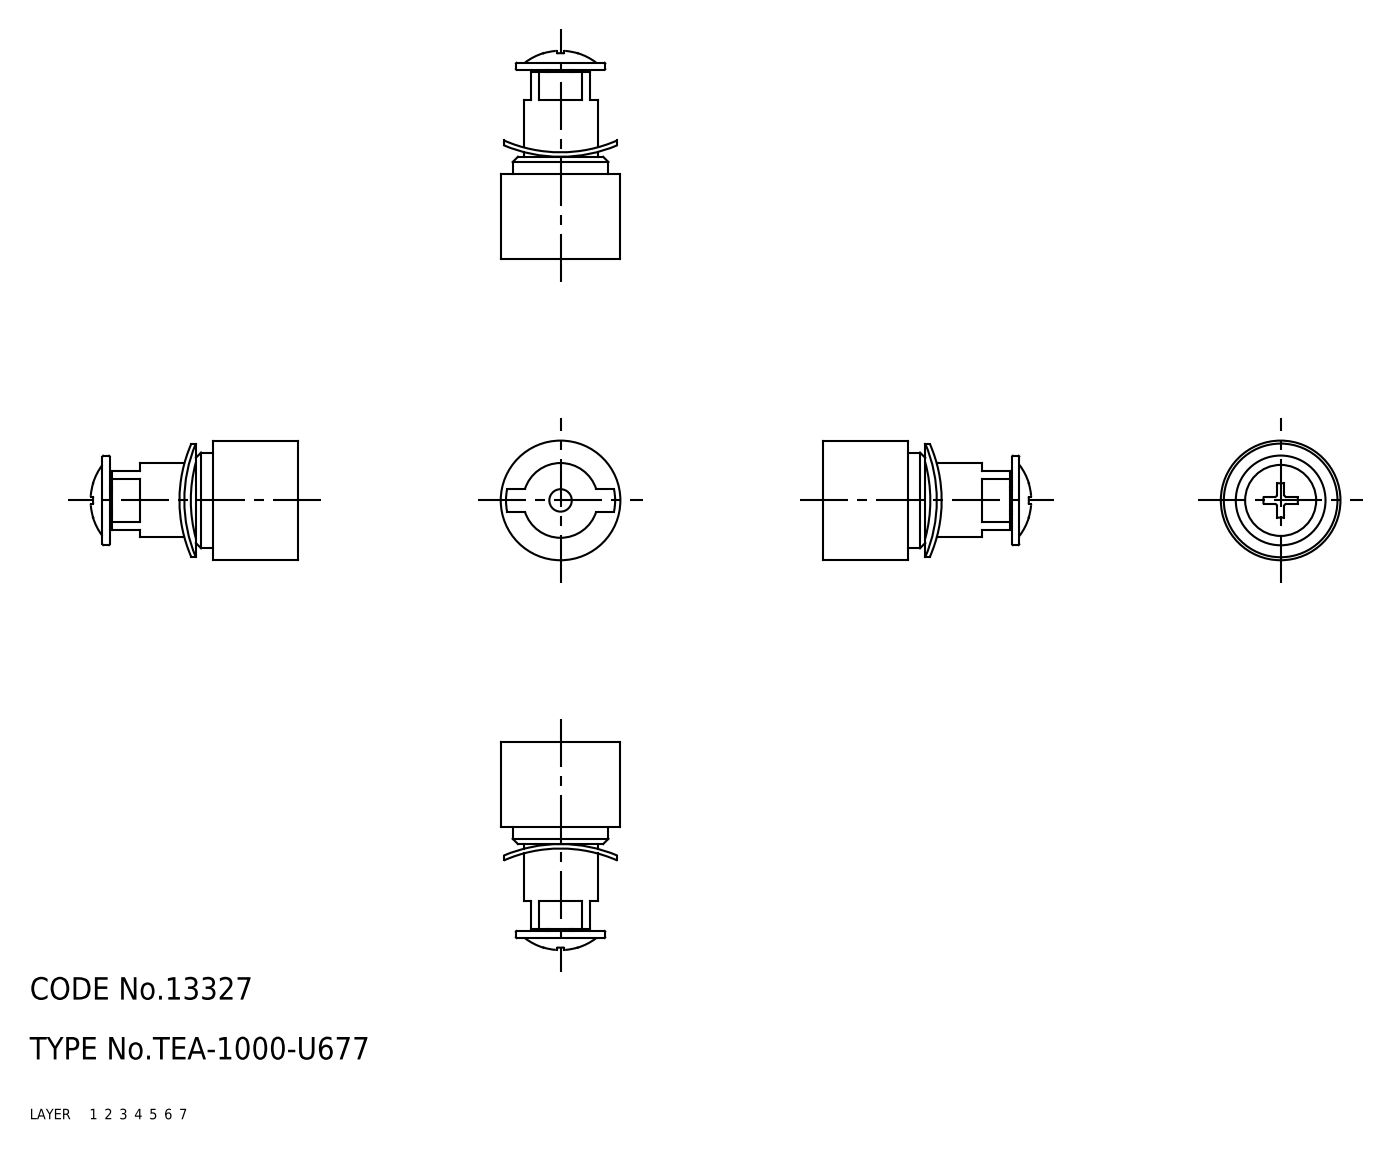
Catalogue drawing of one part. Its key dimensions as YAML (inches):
part_name: "shaft"
step_written_by: "CADfix (AUTOMOTIVE_DESIGN)"
units: inches
bodies: {solids: 1, faces: 68, planar: 0, cylindrical: 0, other: 68}
overall_size: [1.097, 0.63, 0.63]
volume: 0.183
surface_area: 3.266
